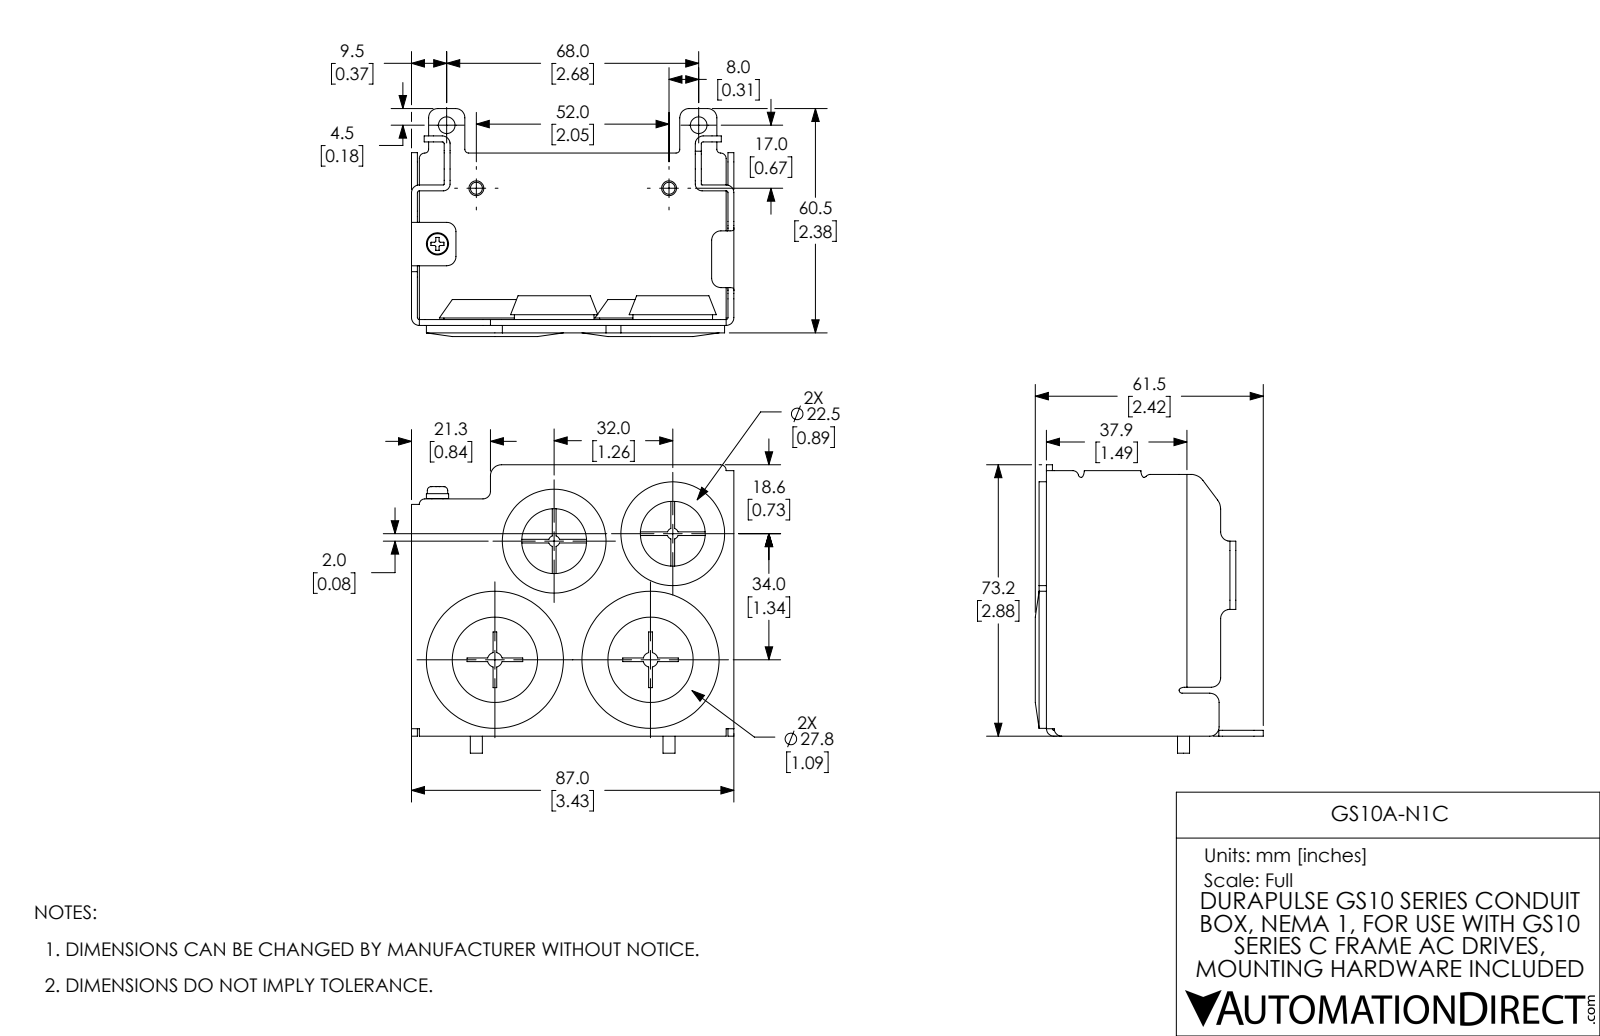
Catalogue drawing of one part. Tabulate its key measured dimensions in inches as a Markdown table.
| quantity | value |
| --- | --- |
| part name | MKME-CBC r1 coord |
| STEP written by | SolidWorks 2017 (AUTOMOTIVE_DESIGN) |
| units | inches |
| bodies | 8 solids, 356 faces (173 planar, 155 cylindrical, 28 other) |
| overall size | 3.425 × 3.063 × 2.421 |
| volume | 2.165 in³ |
| surface area | 69.79 in² |
| round holes (diameter × count) | 0.157 × 2, 0.177 × 2, 0.212 × 2, 0.261 × 2, 0.689 × 2, 0.846 × 2, 0.886 × 2, 1.094 × 2, 0.138 × 1, 0.166 × 1, 0.193 × 1 |
| round bosses / shafts (diameter × count) | 1.457 × 2, 1.102 × 2, 1.083 × 2, 0.846 × 2, 0.128 × 2, 0.236 × 1, 0.217 × 1, 0.118 × 1 |
| partial cylindrical surfaces (radius × count) | 0.098 × 18, 0.059 × 10, 0.02 × 6, 0.083 × 6, 0.031 × 5, 0.079 × 5, 0.008 × 4, 0.012 × 4 |
| main face-to-face distances | 0.063, 3.362, 3.299, 3.425, 0.079, 0.346, 3.016, 0.039, 0.142, 1.429 |
| hole center spacings | 0.74, 2.455, 0.721, 1.262, 1.264, 1.359, 1.409, 1.623 |
